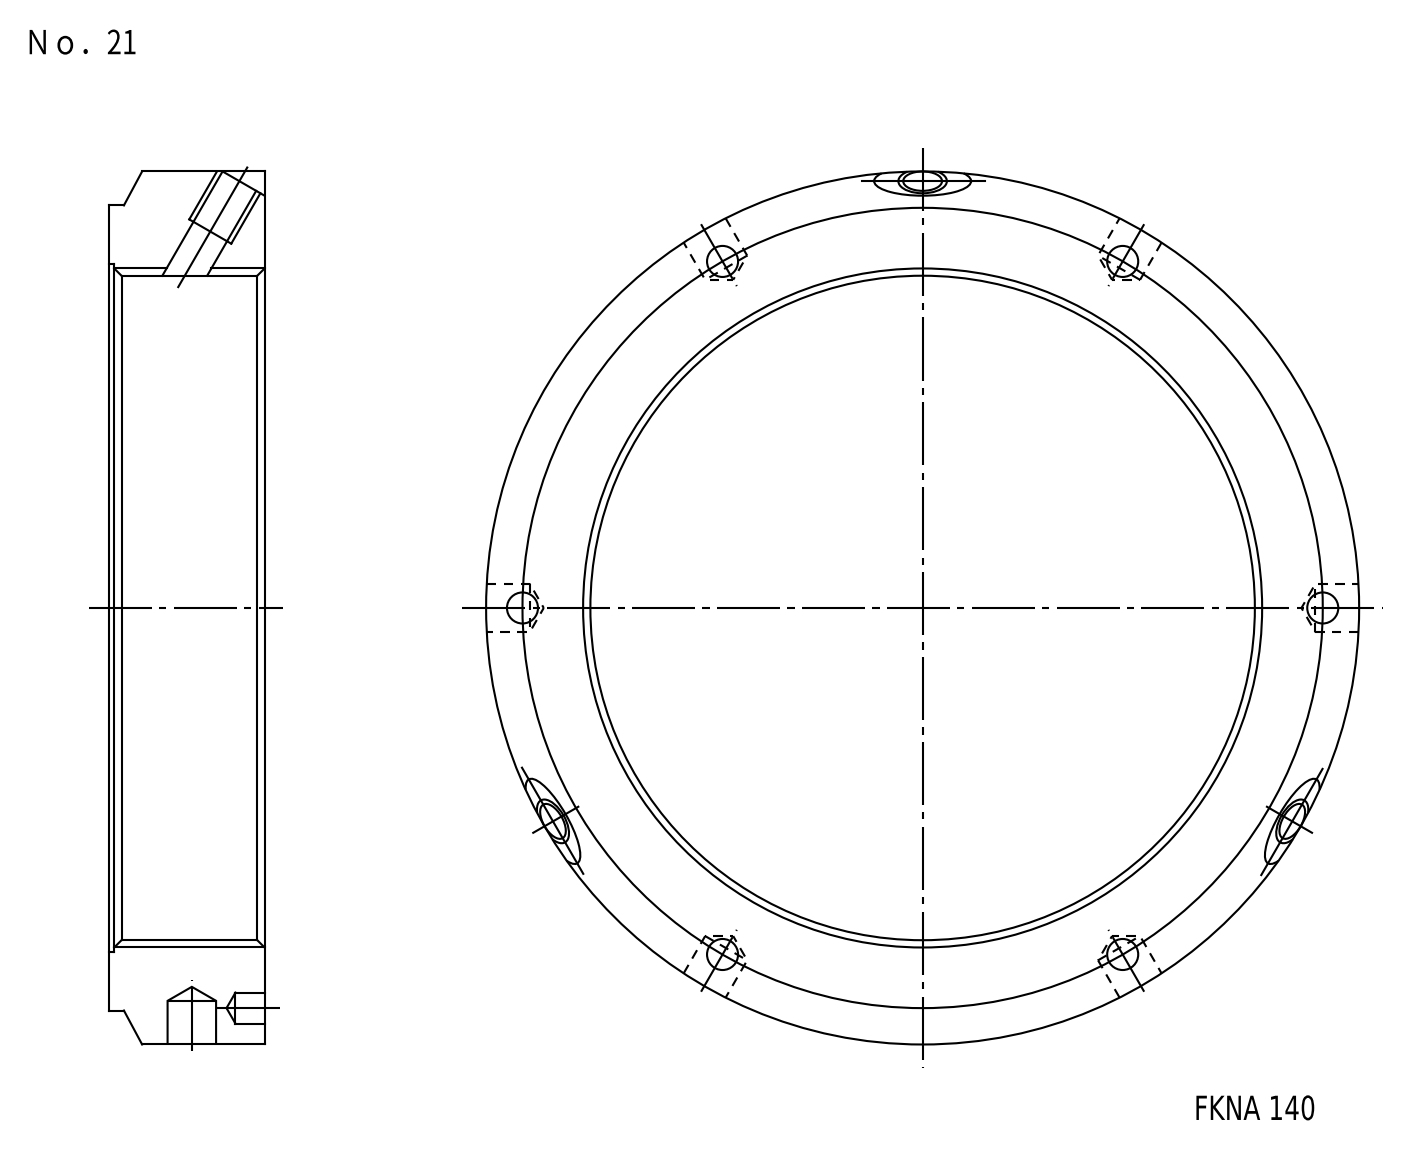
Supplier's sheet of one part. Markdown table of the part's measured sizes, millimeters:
| quantity | value |
| --- | --- |
| part name | FKD FKNA140 |
| STEP written by | Autodesk Inventor LT (CONFIG_CONTROL_DESIGN) |
| units | millimeters |
| bodies | 1 solid, 44 faces (6 planar, 25 cylindrical, 13 other) |
| overall size | 180 × 180 × 32 |
| volume | 299 395 mm³ |
| surface area | 53 877 mm² |
| round holes (diameter × count) | 6.4 × 6, 8.38 × 3, 10 × 3, 10.2 × 3, 140 × 1, 142 × 1 |
| round bosses / shafts (diameter × count) | 180 × 1, 166 × 1 |
| partial cylindrical surfaces (radius × count) | 20 × 3 |
| main face-to-face distances | 32, 1.5, 30.5 |
| hole center spacings | 82.5, 142.9, 165.01, 165 |
